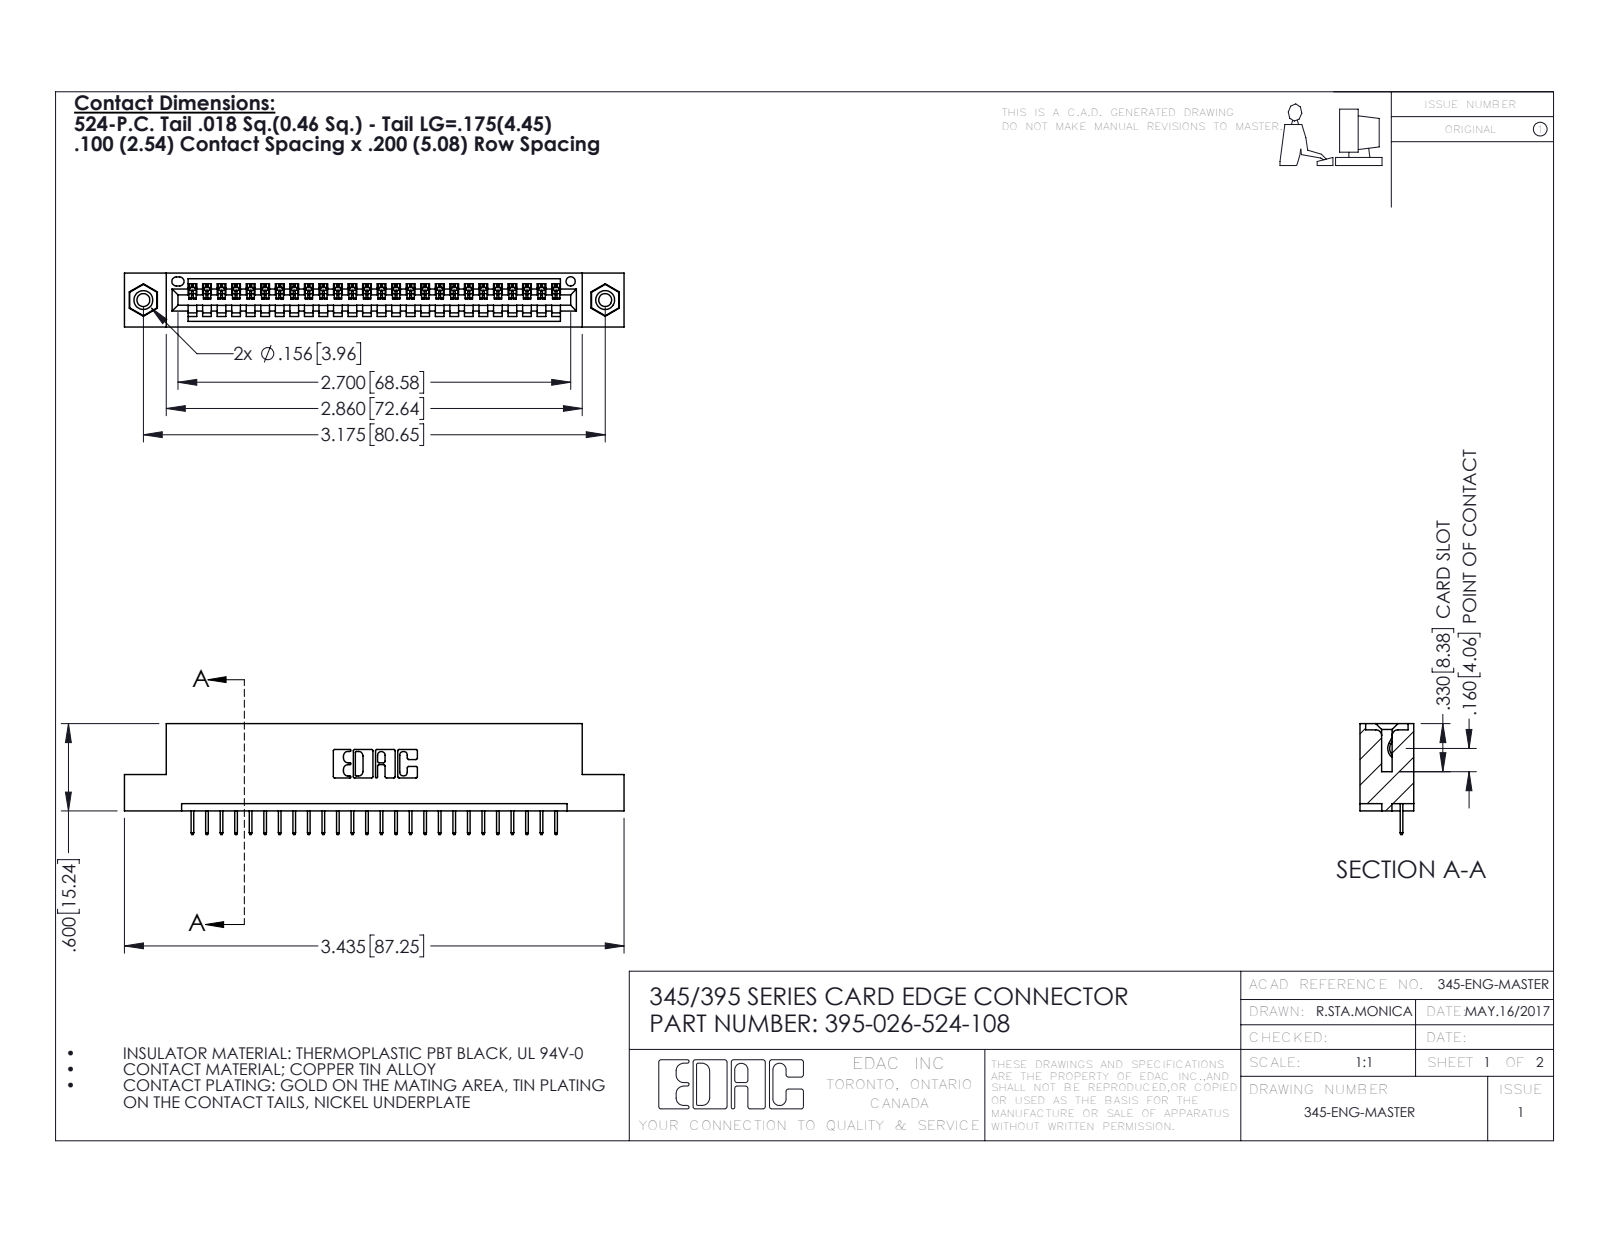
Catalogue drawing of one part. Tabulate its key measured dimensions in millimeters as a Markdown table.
| quantity | value |
| --- | --- |
| part name | 395-026-524-108; 345-292-001_345-293-124; 345-250-001_345-250-003-102; 345 Part_Flush Mounting Lugs - 0.156 Dia-TI |
| STEP written by | SolidWorks 2016 (CONFIG_CONTROL_DESIGN) |
| units | millimeters |
| bodies | 29 solids, 1798 faces (1308 planar, 474 cylindrical, 16 other) |
| overall size | 87.2 × 19.4 × 9.4 |
| volume | 8 050 mm³ |
| surface area | 10 170 mm² |
| round holes (diameter × count) | 2.3 × 2, 3.2 × 2, 4 × 2, 1.6 × 1 |
| round bosses / shafts (diameter × count) | 3.9 × 2 |
| partial cylindrical surfaces (radius × count) | 0.2 × 52, 0.3 × 22, 0.2 × 6, 0.8 × 6, 0.7 × 3, 0.8 × 2, 1 × 2, 0.4 × 1 |
| main face-to-face distances | 1.8, 7.6, 9.4, 5.1, 2.5, 6.9, 0.6, 5.7, 1.8, 3.8 |
| hole center spacings | 6.9, 74.7, 80.6 |
